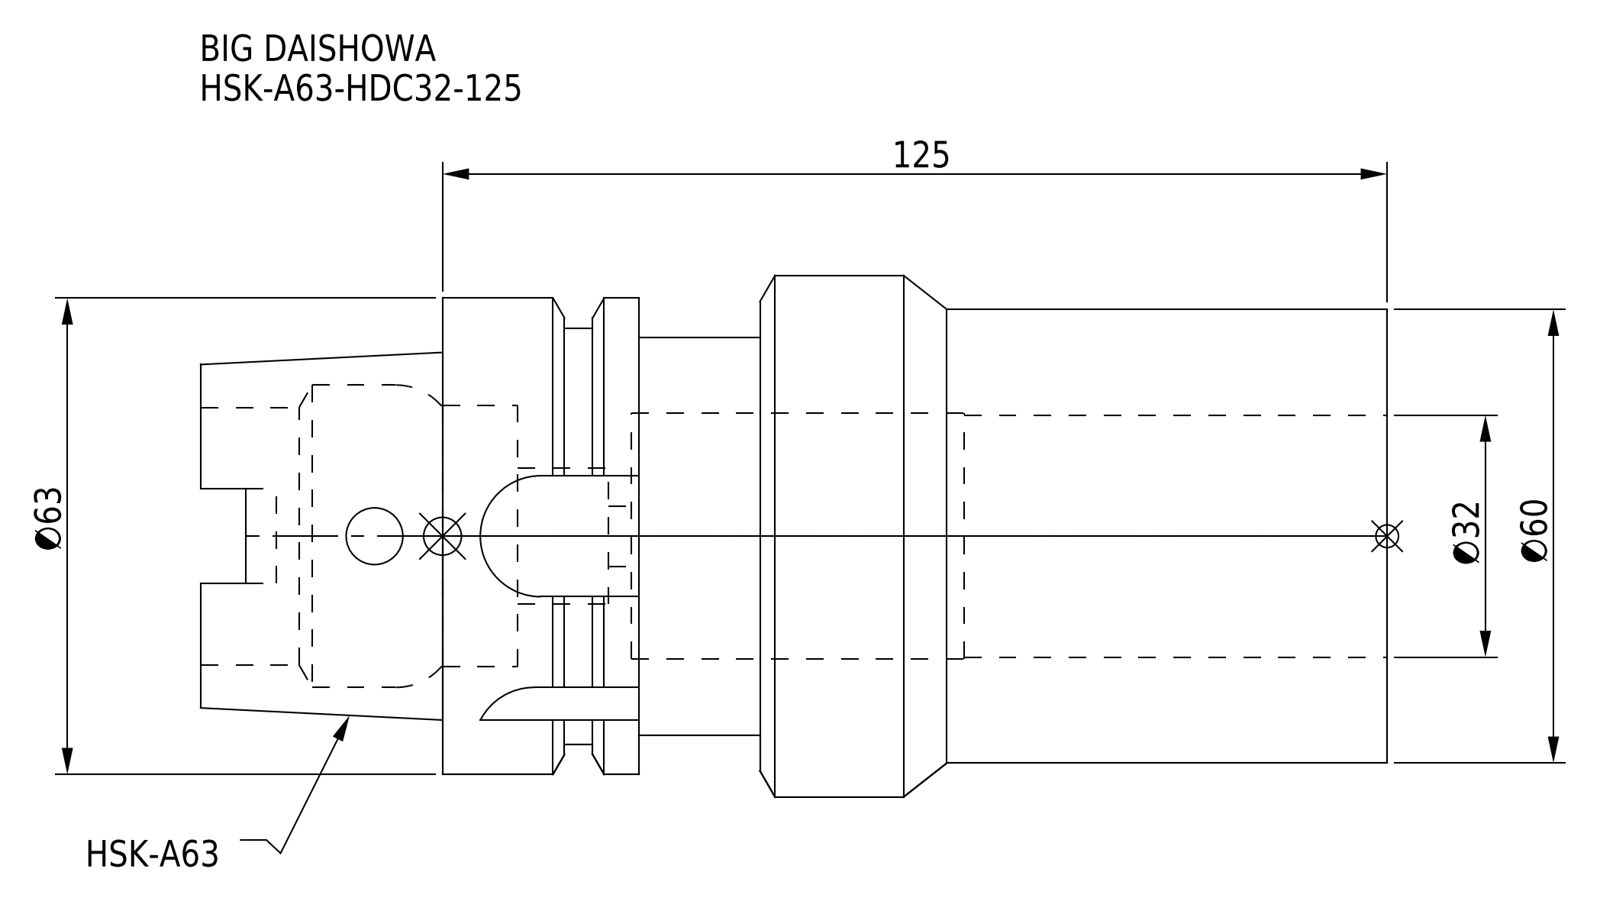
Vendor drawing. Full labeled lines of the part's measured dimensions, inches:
Part name (STEP PRODUCT): HSK-A63-HDC32-125
STEP written by: CREO PARAMETRIC BY PTC INC, 2016380 (AUTOMOTIVE_DESIGN)
Units: inches
Bodies: 1 solid, 98 faces (39 planar, 41 cylindrical, 18 other)
Overall size (bounding box): 6.181 × 2.717 × 2.717
Volume: 17.62 in³ · Surface area: 83.06 in²
Round holes (diameter × count): ⌀0.295 ×1, ⌀0.315 ×1, ⌀0.709 ×1, ⌀1.26 ×1, ⌀1.28 ×1, ⌀1.339 ×1, ⌀1.358 ×1, ⌀1.575 ×1
Round bosses / shafts (diameter × count): ⌀2.717 ×1, ⌀2.48 ×1, ⌀2.362 ×1, ⌀2.165 ×1, ⌀2.071 ×1
Partial cylindrical surfaces — rounded edges, fillets, slot ends (radius × count): R0.113 ×4, R0.315 ×4
Main face-to-face distances: 4.921, 1.024, 3.268, 1.654, 0.669, 0.039, 0.63, 3.937, 0.984, 3.898
